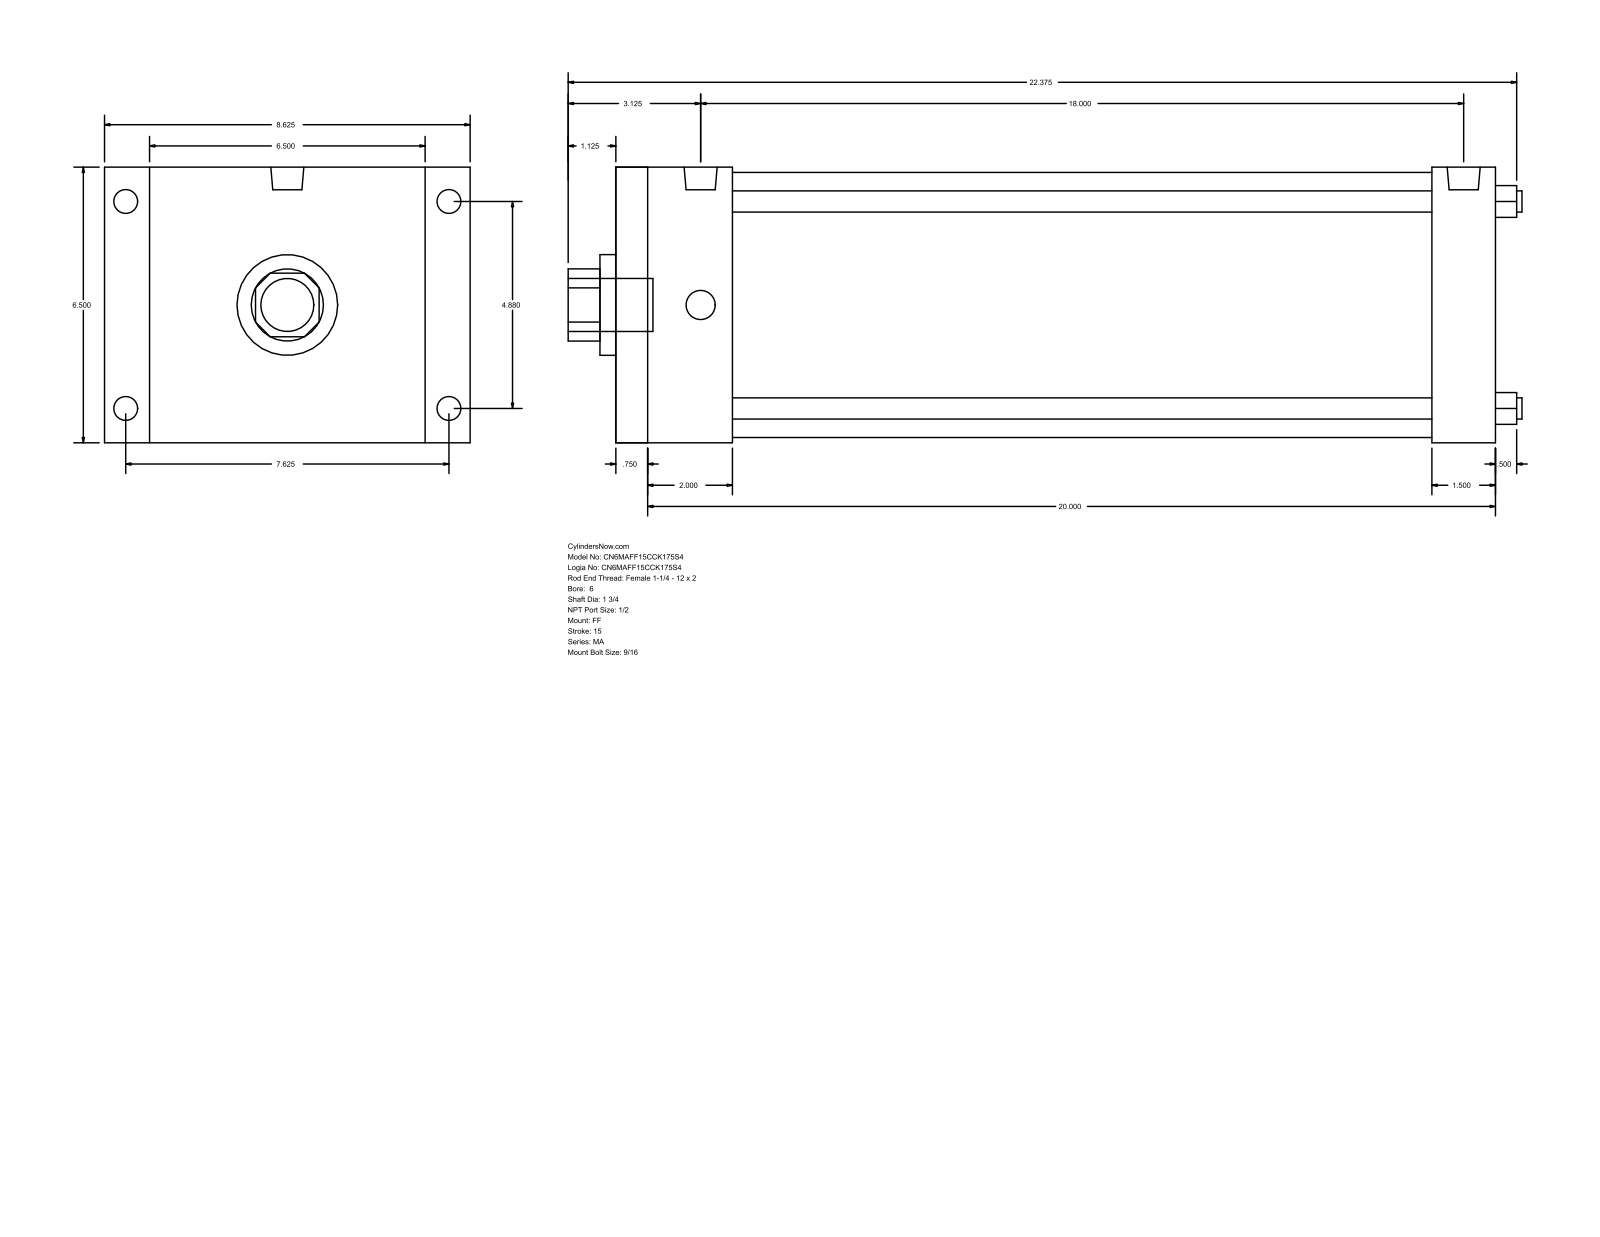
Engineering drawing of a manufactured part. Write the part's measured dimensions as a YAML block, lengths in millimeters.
part_name: "MA_FF__0600_1.75"
step_written_by: "GSSL Pune (CONFIG_CONTROL_DESIGN)"
units: millimeters
bodies: {solids: 0, faces: 92, planar: 64, cylindrical: 28, other: 0}
overall_size: [571.5, 219.07, 165.1]
round_holes:
  - {diameter: 12.7, count: 4}
  - {diameter: 44.45, count: 1}
  - {diameter: 60.33, count: 1}
  - {diameter: 158.75, count: 1}
round_bosses_or_shafts:
  - {diameter: 17.46, count: 4}
  - {diameter: 14.29, count: 4}
  - {diameter: 19.77, count: 2}
  - {diameter: 31.75, count: 1}
partial_cylinders:
  - {radius: 21.63, count: 1}
face_to_face_distances: [165.1, 527.05, 19.05, 508, 38.1, 50.8, 69.85, 457.2, 488.95, 469.9]
hole_center_spacings: [87.65, 123.96, 175.31]
